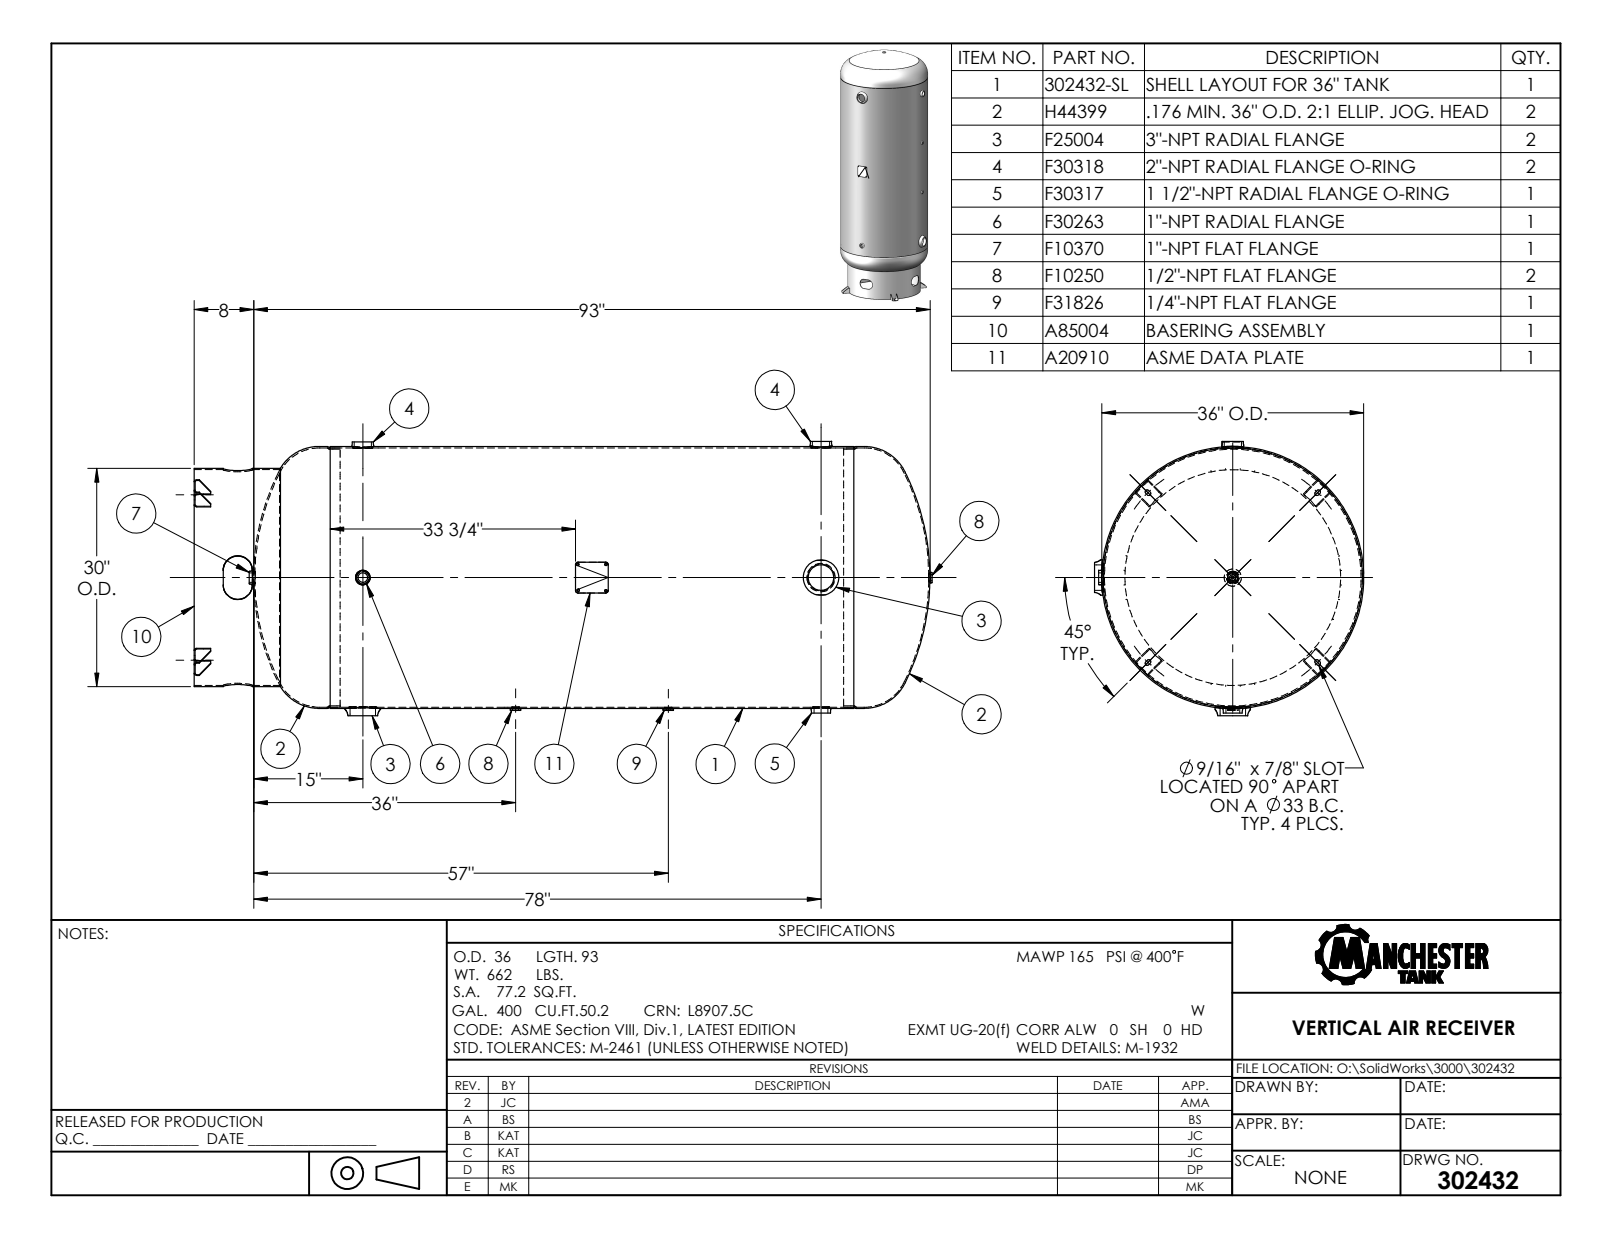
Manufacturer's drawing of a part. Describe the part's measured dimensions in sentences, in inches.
The part is named "302432". Its 3-D file was written by "SolidWorks 2011 (CONFIG_CONTROL_DESIGN)". It is 0 solids with 271 faces: 88 planar, 86 cylindrical and 97 other. Overall it measures 101.78 by 37.862 by 37 inches. Round holes: 2 of diameter 0.84, 2 of diameter 2.375, 2 of diameter 3.5, 1 of diameter 0.54, 1 of diameter 1.315, 1 of diameter 1.315, 1 of diameter 1.9, 1 of diameter 29.546, 1 of diameter 35.658. Round bosses or shafts: 2 of diameter 4.25, 2 of diameter 3.625, 2 of diameter 2.375, 2 of diameter 1.813, 1 of diameter 36, 1 of diameter 35.62, 1 of diameter 30, 1 of diameter 2.688. Partial cylindrical surfaces (rounded edges, fillets, slot ends): 8 of radius 0.25, 8 of radius 0.384, 7 of radius 0.281, 1 of radius 18.06. The main face-to-face distances are 0.134, 2.446, 0.063, 11.875, 6.936, 18.811, 72, 78.936, 90.811, 90.677. The hole center spacings are 21, 42, 63.
